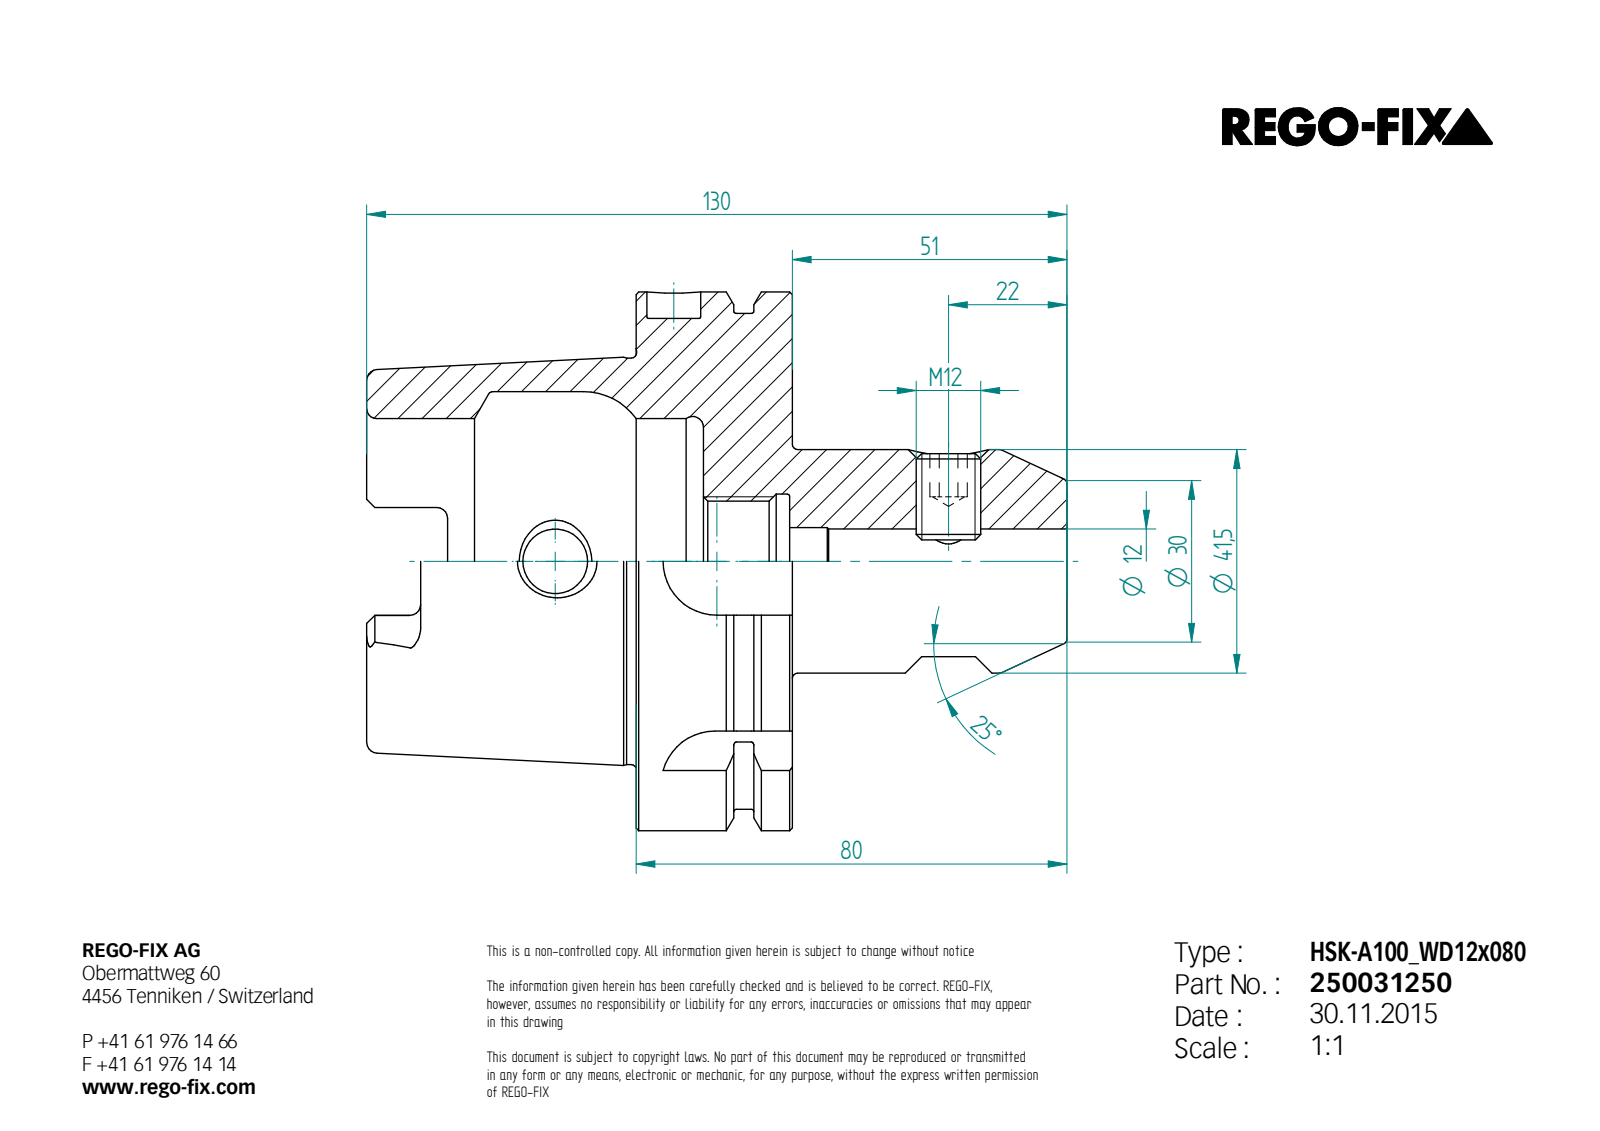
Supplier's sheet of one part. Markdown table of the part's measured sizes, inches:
| quantity | value |
| --- | --- |
| STEP written by | Unknown (AUTOMOTIVE_DESIGN) |
| units | inches |
| bodies | 2 solids, 145 faces (52 planar, 36 cylindrical, 57 other) |
| overall size | 5.118 × 3.937 × 3.937 |
| volume | 19.09 in³ |
| surface area | 90.53 in² |
| round holes (diameter × count) | 0.472 × 2, 0.335 × 1, 0.394 × 1, 0.398 × 1, 0.492 × 1, 0.881 × 1, 0.984 × 1, 2.087 × 1, 2.48 × 1 |
| round bosses / shafts (diameter × count) | 3.937 × 1, 3.622 × 1, 2.971 × 1, 1.634 × 1, 0.472 × 1 |
| partial cylindrical surfaces (radius × count) | 0.079 × 6, 0.192 × 4, 0.394 × 2, 0.433 × 1 |
| main face-to-face distances | 1.142, 0.492, 0.65, 1.969, 2.461, 3.11, 5.118, 3.15, 2.657, 2.008 |
| hole center spacings | 2.008 |
